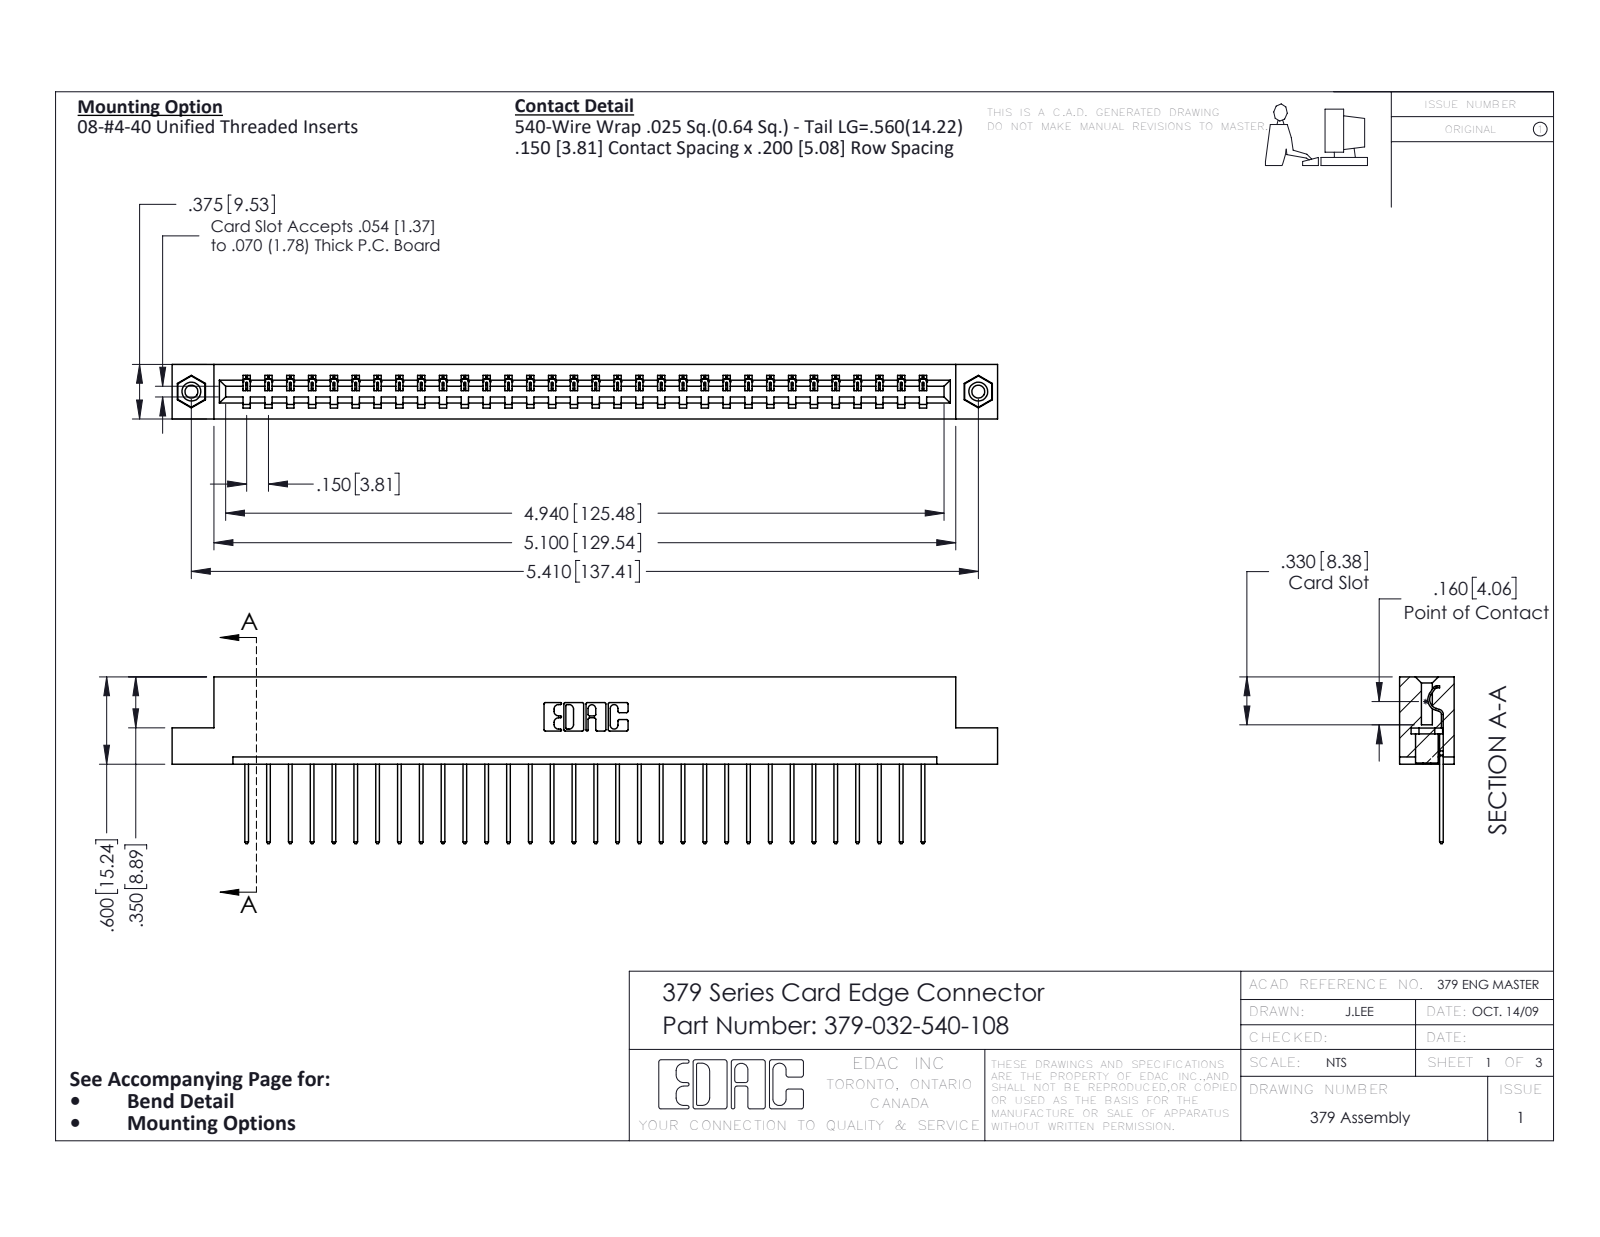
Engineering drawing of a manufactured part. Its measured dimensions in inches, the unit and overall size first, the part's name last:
Units: inches
Overall size (bounding box): 5.675 × 1.147 × 0.375
Round holes (diameter × count): ⌀0.089 ×2, ⌀0.125 ×2, ⌀0.156 ×2
Round bosses / shafts (diameter × count): ⌀0.155 ×2
Partial cylindrical surfaces — rounded edges, fillets, slot ends (radius × count): R0.006 ×64, R0.01 ×64, R0.01 ×22, R0.007 ×6, R0.031 ×6, R0.026 ×3, R0.014 ×1, R0.022 ×1
Main face-to-face distances: 0.3, 0.075, 0.375, 0.225, 0.275, 0.1, 0.025, 0.2, 0.6, 0.55
Hole centre spacings: 5.41
Volume: 0.919 in³ · Surface area: 24.36 in²
Bodies: 35 solids, 2030 faces (1446 planar, 568 cylindrical, 16 other)
Part name (STEP PRODUCT): 345-292-001_345-293-140; 379 Part_Flush - .156 Dia - TI; 345-250-001_345-250-003-102; 379-032-540-108
STEP written by: SolidWorks 2016 (CONFIG_CONTROL_DESIGN)
